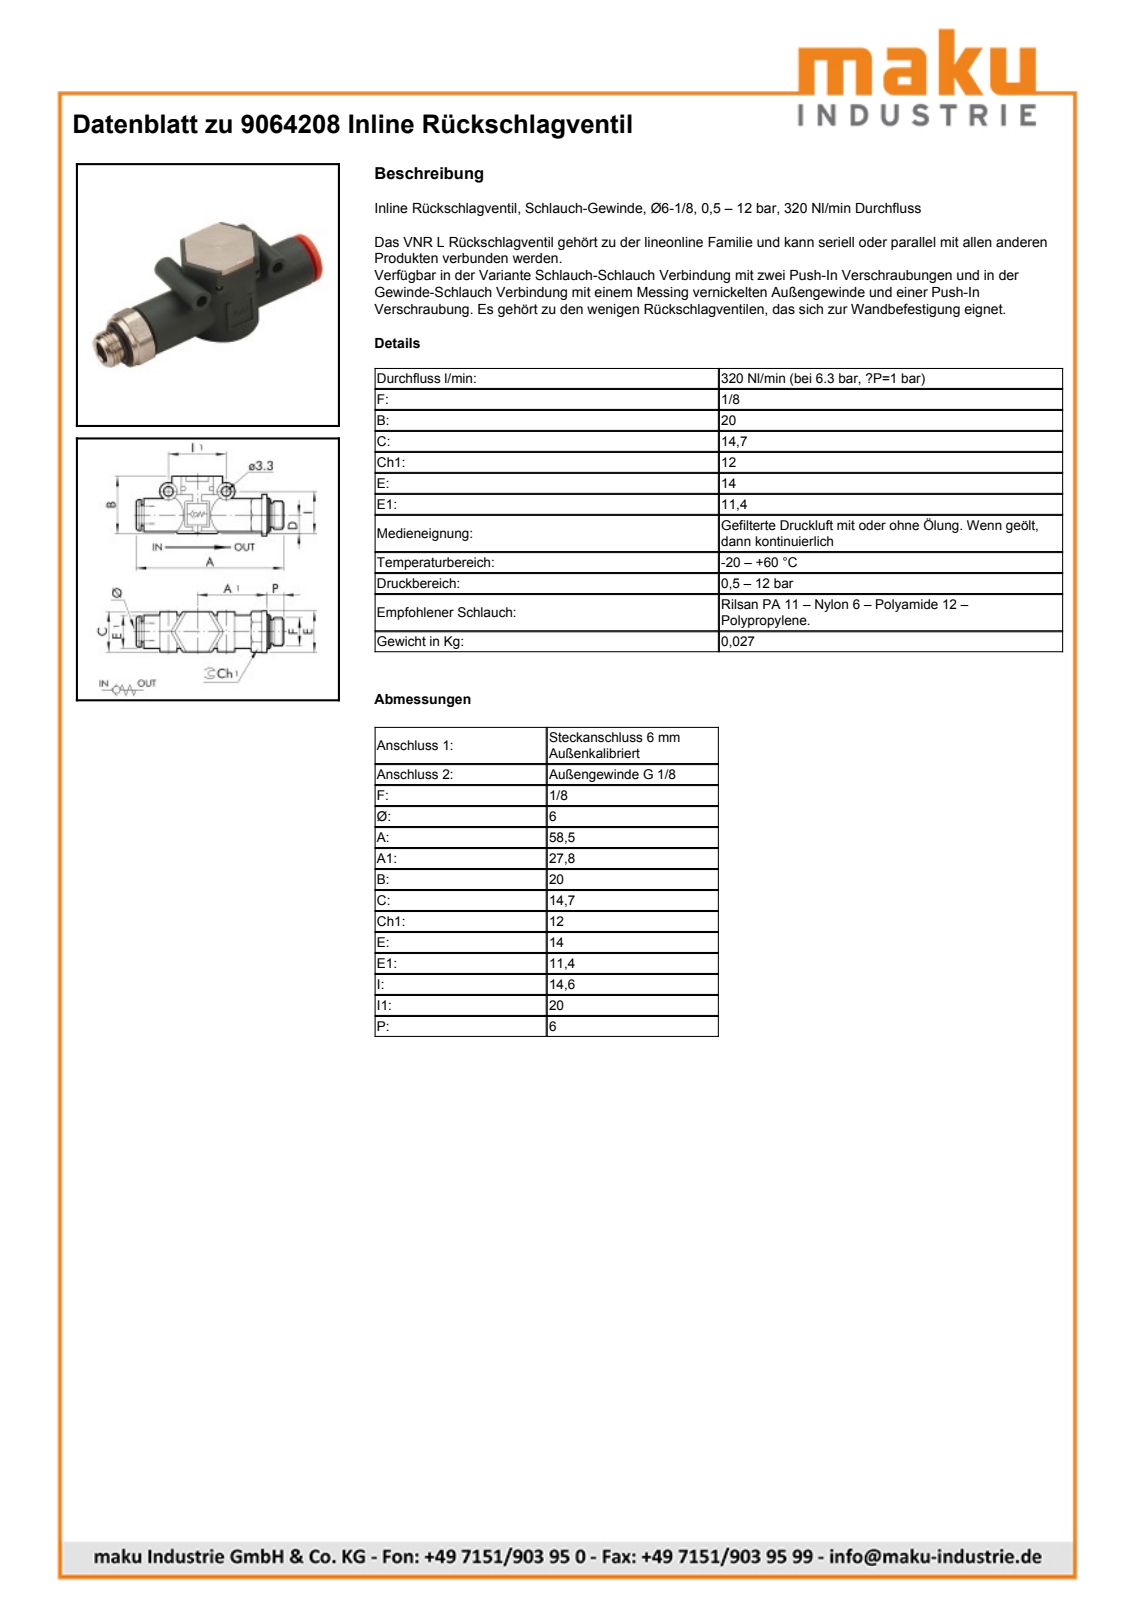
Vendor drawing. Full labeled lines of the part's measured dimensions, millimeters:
Part name (STEP PRODUCT): 9064208; LINE-ON-LINE D6 VSR-L body; LINE-ON-LINE D6-1/8 thread port; LINE-ON-LINE D6 VNR-L bushing (+1 more)
STEP written by: PARTsolutions (AUTOMOTIVE_DESIGN)
Units: millimetres
Bodies: 4 solids, 157 faces (95 planar, 51 cylindrical, 11 other)
Overall size (bounding box): 58 × 20.6 × 14.7
Volume: 5 218 mm³ · Surface area: 6 780 mm²
Round holes (diameter × count): ⌀3.3 ×2, ⌀3.5 ×1, ⌀4 ×1, ⌀5 ×1, ⌀6 ×1, ⌀6.2 ×1, ⌀7.4 ×1, ⌀9 ×1, ⌀9.6 ×1, ⌀10.3 ×1, ⌀11.6 ×1
Round bosses / shafts (diameter × count): ⌀6 ×2, ⌀14.8 ×1, ⌀14 ×1, ⌀11.4 ×1, ⌀11 ×1, ⌀9.73 ×1, ⌀8.2 ×1, ⌀8.1 ×1
Partial cylindrical surfaces — rounded edges, fillets, slot ends (radius × count): R3.75 ×1, R6.85 ×1, R7.9 ×1, R7.95 ×1, R9.15 ×1
Main face-to-face distances: 1.6, 18.6, 1.4, 18.4, 20, 1.04, 17, 12.1, 29.9, 0.4
Hole centre spacings: 12.74, 20
